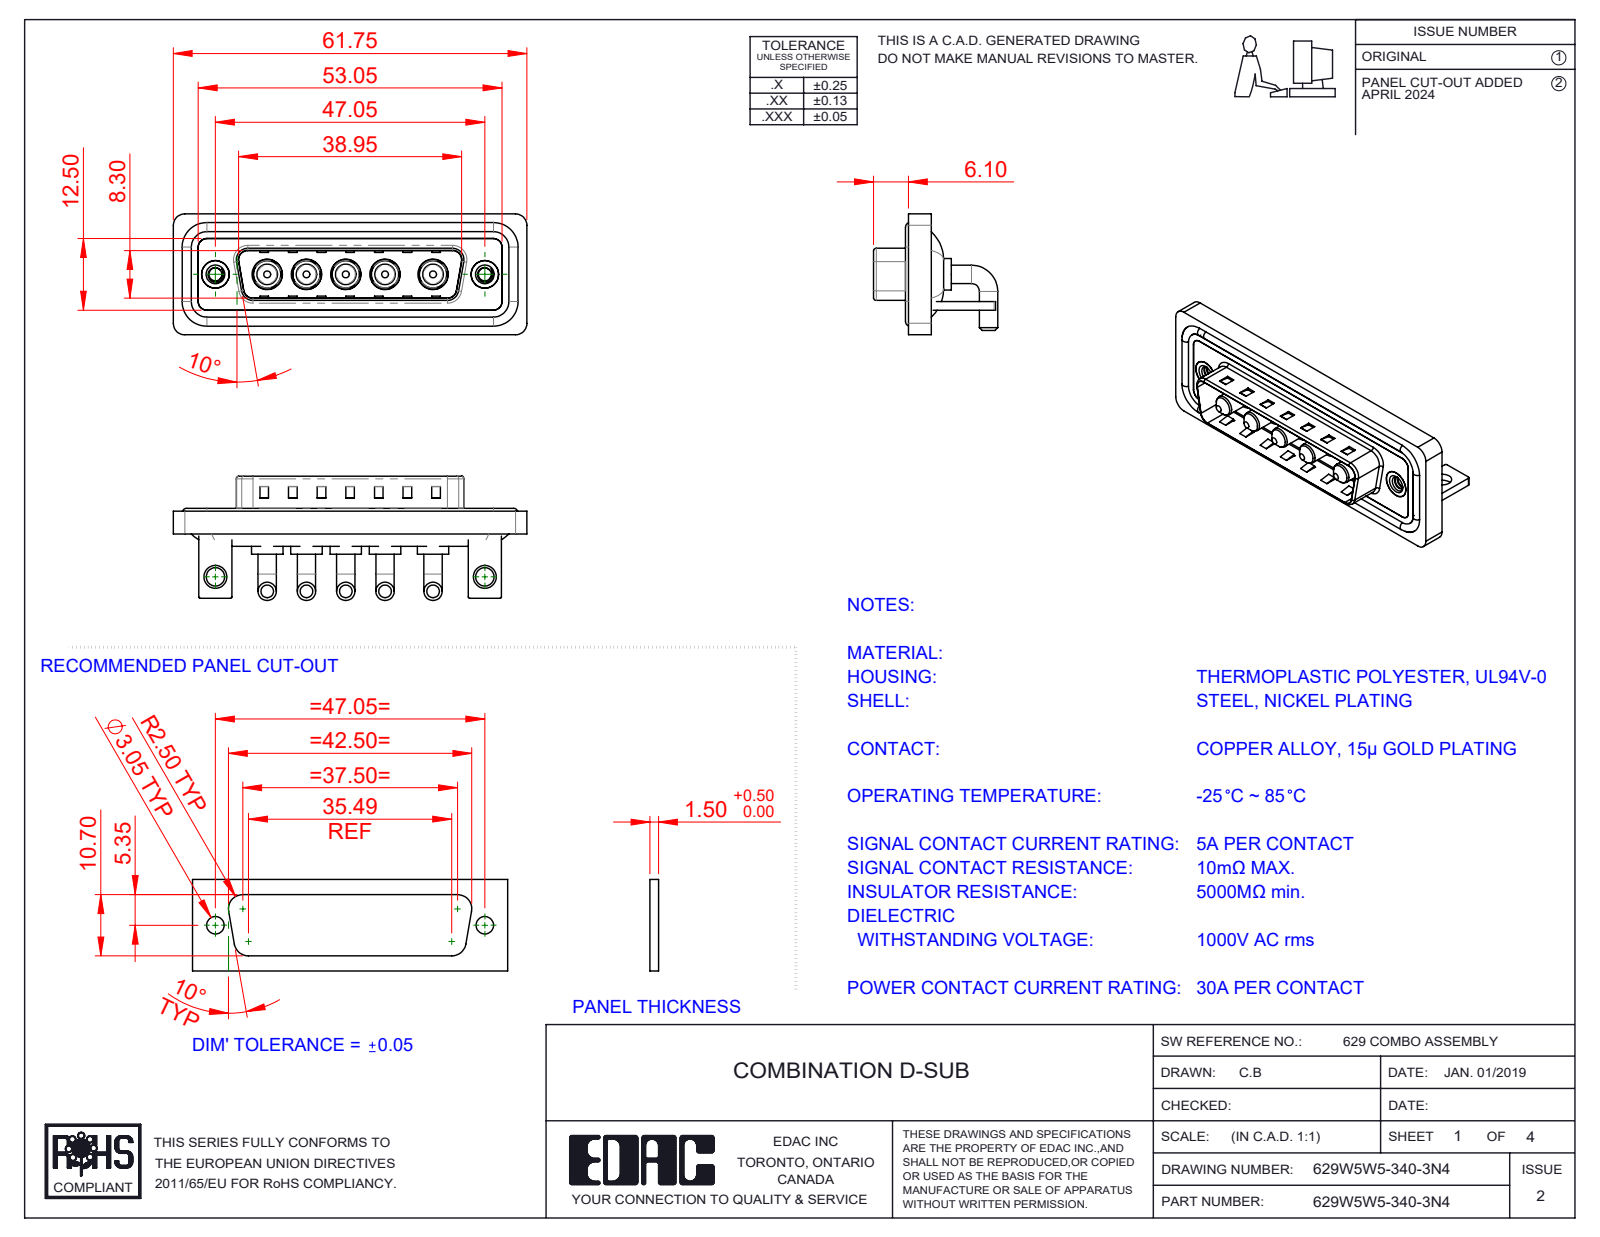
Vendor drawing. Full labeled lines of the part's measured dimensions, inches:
Part name (STEP PRODUCT): 629W5W5-340-3N4; 629Combo Waterproof Housing_25 Contacts; 629Combo Shell Rear_25 Contacts; Power Pin_30A RA (+4 more)
STEP written by: SolidWorks 2023 (CONFIG_CONTROL_DESIGN)
Units: inches
Bodies: 19 solids, 738 faces (279 planar, 311 cylindrical, 148 other)
Overall size (bounding box): 2.431 × 0.854 × 0.831
Volume: 0.502 in³ · Surface area: 20.07 in²
Round holes (diameter × count): ⌀0.191 ×5, ⌀0.209 ×5, ⌀0.089 ×2, ⌀0.126 ×2, ⌀0.157 ×2, ⌀0.189 ×2, ⌀0.197 ×2
Round bosses / shafts (diameter × count): ⌀0.126 ×10, ⌀0.217 ×5, ⌀0.205 ×5, ⌀0.187 ×5, ⌀0.148 ×5, ⌀0.142 ×5, ⌀0.063 ×4, ⌀0.193 ×2
Partial cylindrical surfaces — rounded edges, fillets, slot ends (radius × count): R0.079 ×19, R0.059 ×18, R0.01 ×16, R0.02 ×9, R0.063 ×8, R0.083 ×5, R0.024 ×4, R0.026 ×4
Main face-to-face distances: 0.016, 0.059, 0.114, 0.031, 0.083, 0.043, 0.146, 0.177, 0.161, 0.047
Hole centre spacings: 0.27, 0.541, 1.852, 0.27, 0.27, 0.33, 0.33, 0.356
